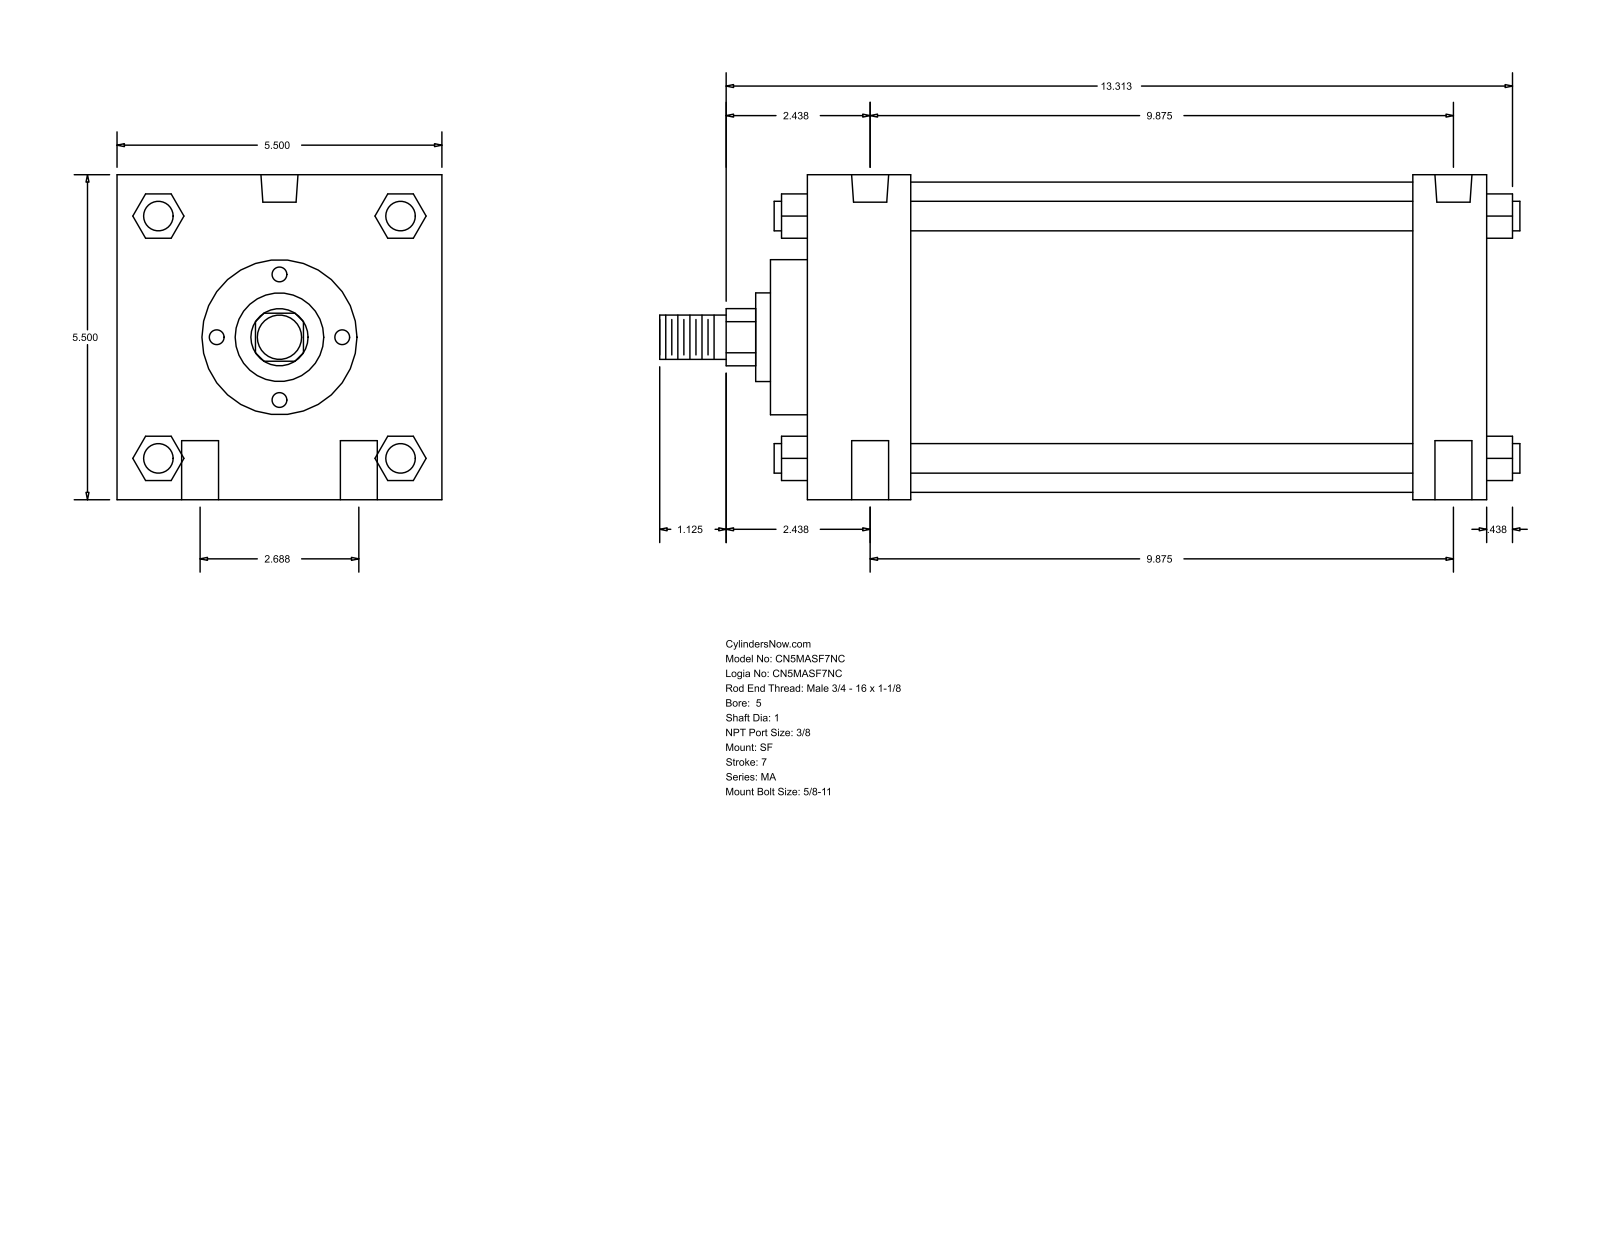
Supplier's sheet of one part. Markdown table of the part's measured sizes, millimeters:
| quantity | value |
| --- | --- |
| part name | MA_SF__0500_1 |
| STEP written by | GSSL Pune (CONFIG_CONTROL_DESIGN) |
| units | millimeters |
| bodies | 0 solids, 126 faces (95 planar, 31 cylindrical, 0 other) |
| overall size | 369.89 × 139.7 × 139.7 |
| round holes (diameter × count) | 15.88 × 4, 11.11 × 2, 15.93 × 2 |
| round bosses / shafts (diameter × count) | 12.7 × 4, 133.35 × 1, 66.67 × 1, 38.1 × 1, 25.4 × 1, 19.05 × 1 |
| partial cylindrical surfaces (radius × count) | 12.29 × 1 |
| main face-to-face distances | 139.7, 292.1, 44.46, 260.35, 215.89, 247.64, 31.75, 15.87, 60.33, 276.22 |
| hole center spacings | 34.13, 253.14, 250.83, 68.26, 259.95, 241.31 |
